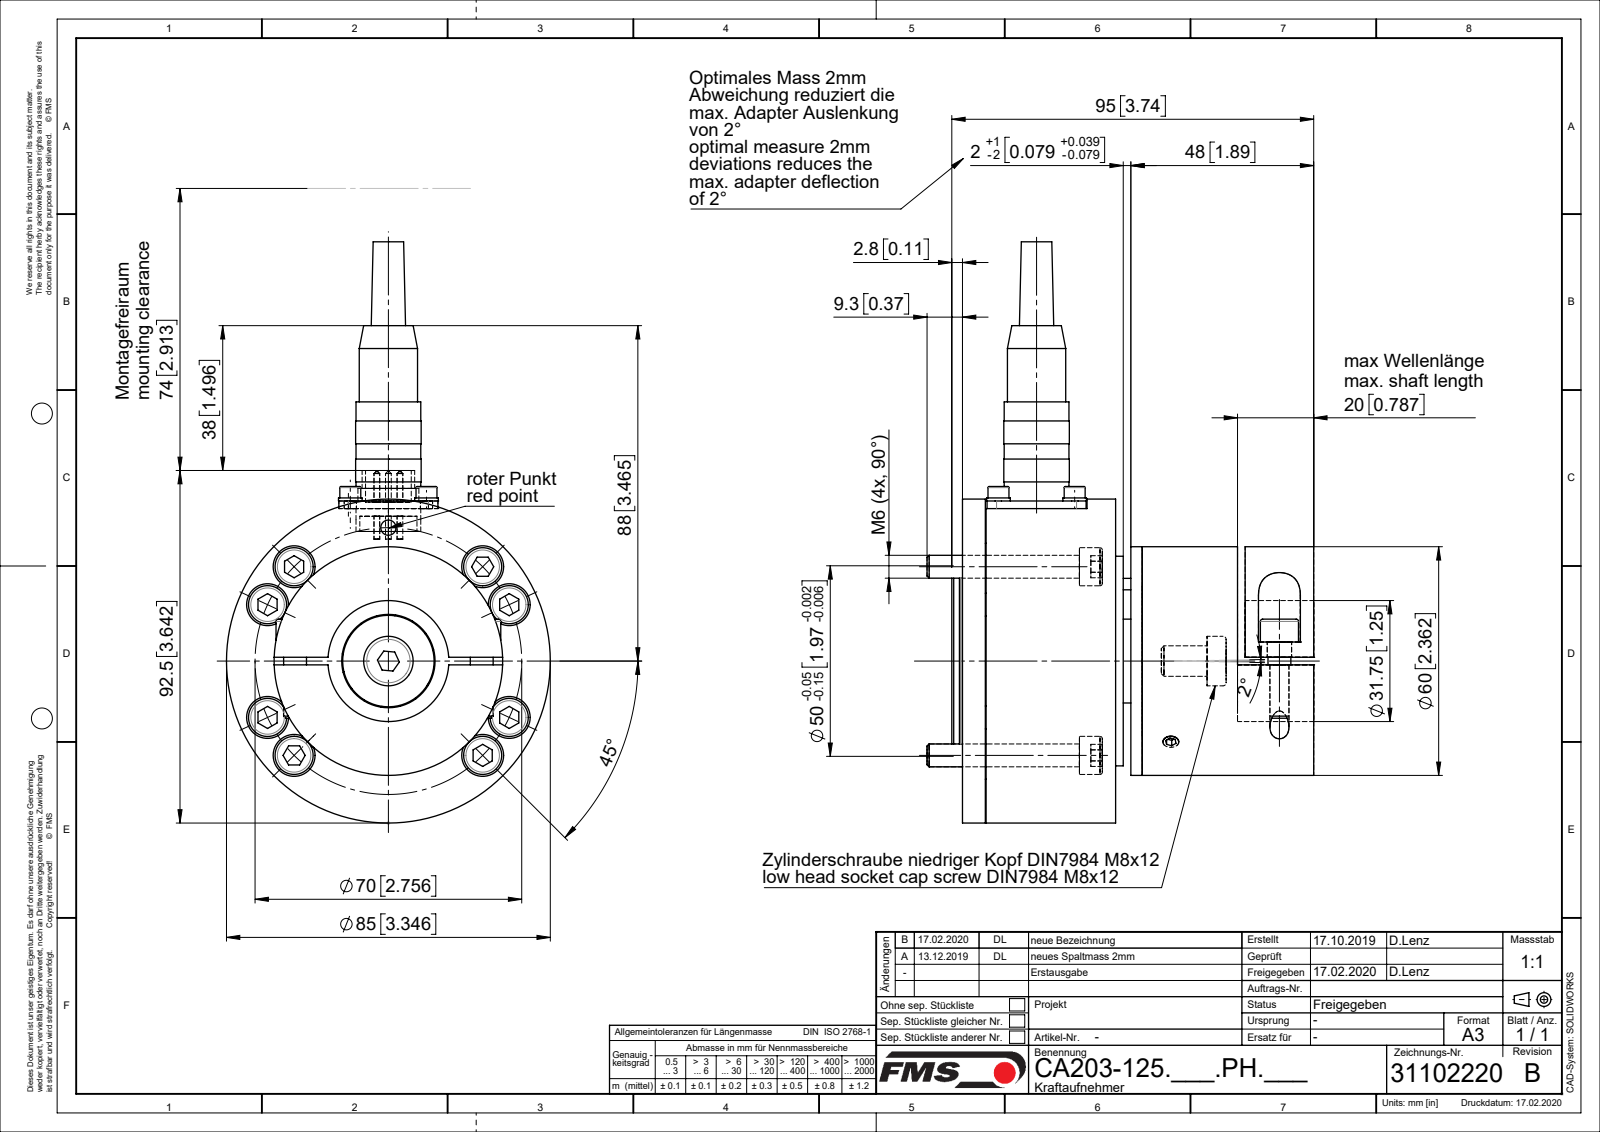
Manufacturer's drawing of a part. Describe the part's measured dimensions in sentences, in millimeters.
The part is named "ZEICHNUNG9; C50331_DI125; C0709081; C0612056 (+8 more)". Its 3-D file was written by "Mechanical Desktop 2009 (CONFIG_CONTROL_DESIGN)". It is 38 solids with 744 faces: 266 planar, 326 cylindrical and 152 other. Overall it measures 152.5 by 101 by 85 millimeters. Its volume is 291 195 cubic millimeters and its surface area 108 543 square millimeters. Round holes: 8 of diameter 2.6, 8 of diameter 6.5, 8 of diameter 11, 6 of diameter 5.15, 4 of diameter 3.2, 4 of diameter 3.6, 4 of diameter 4, 4 of diameter 7, 2 of diameter 6.4, 1 of diameter 3, 1 of diameter 4.33, 1 of diameter 7.15. Round bosses or shafts: 14 of diameter 6, 10 of diameter 10, 8 of diameter 3, 5 of diameter 1.5, 4 of diameter 6.2, 4 of diameter 5.5, 4 of diameter 5, 1 of diameter 85. Partial cylindrical surfaces (rounded edges, fillets, slot ends): 10 of radius 4, 4 of radius 2.5, 2 of radius 5, 2 of radius 5.5. The main face-to-face distances are 11.5, 6, 46.5, 2, 31.5, 1.5, 45, 6.5, 3, 49.5. The hole center spacings are 24.78, 25.2, 56.46, 20, 32.8, 35, 51.14, 28.28.
